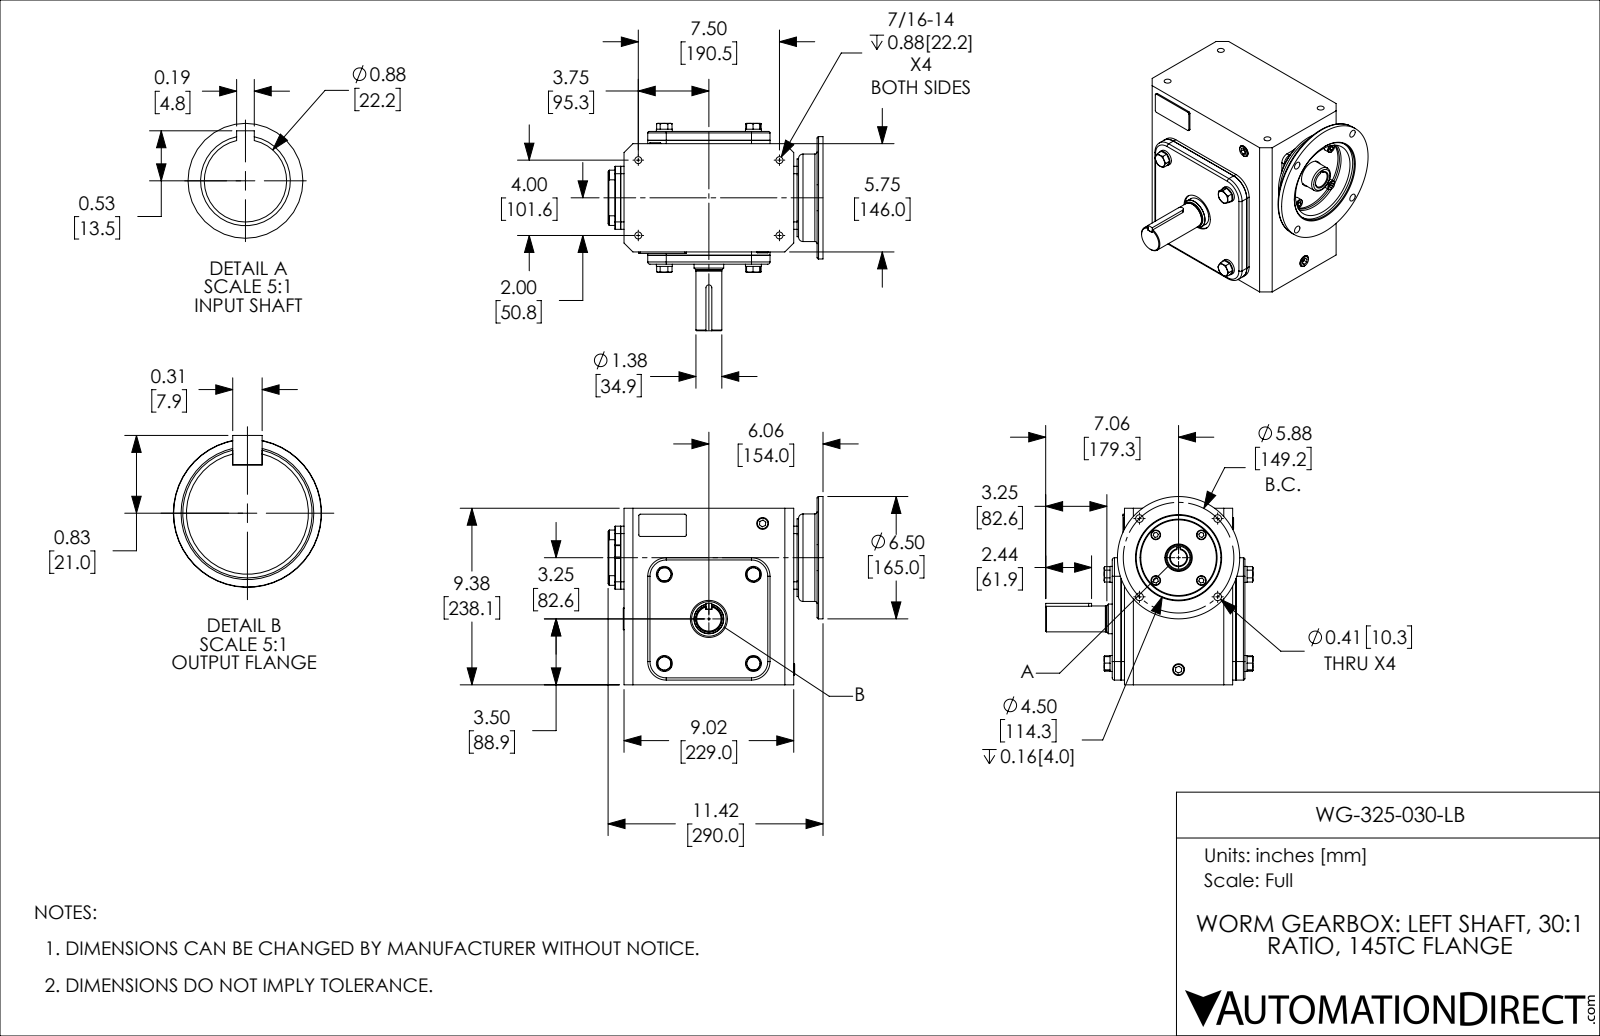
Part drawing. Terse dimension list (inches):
name: WG-325-030-LB
written by: SolidWorks 2017 (AUTOMOTIVE_DESIGN)
unit: in
bodies: 39 solids, 575 faces (318 planar, 167 cylindrical, 90 other)
size: 11.417 × 11.014 × 9.998
volume: 504 in³; area: 902.4 in²
holes: 4× ⌀0.368, 4× ⌀0.406, 3× ⌀0.628, 1× ⌀0.591, 1× ⌀0.875, 1× ⌀0.978, 1× ⌀1.181, 1× ⌀1.457, 1× ⌀1.969, 1× ⌀2.441, 1× ⌀2.756, 1× ⌀4.016
bosses: 4× ⌀0.846, 4× ⌀0.512, 1× ⌀6.496, 1× ⌀4.646, 1× ⌀4.134, 1× ⌀2.835, 1× ⌀1.575, 1× ⌀1.378
rounds: 11× R0.079, 4× R0.118, 4× R0.394, 4× R0.906, 4× R0.984, 2× R0.02, 2× R0.039, 1× R0.156
face distances: 0.079, 0.177, 6.496, 0.394, 6.969, 0.472, 6.575, 6.398, 0.571, 0.65
hole spacings: 2.937, 4.154, 2.385, 4, 4.389, 5.718, 5.817, 5.875
